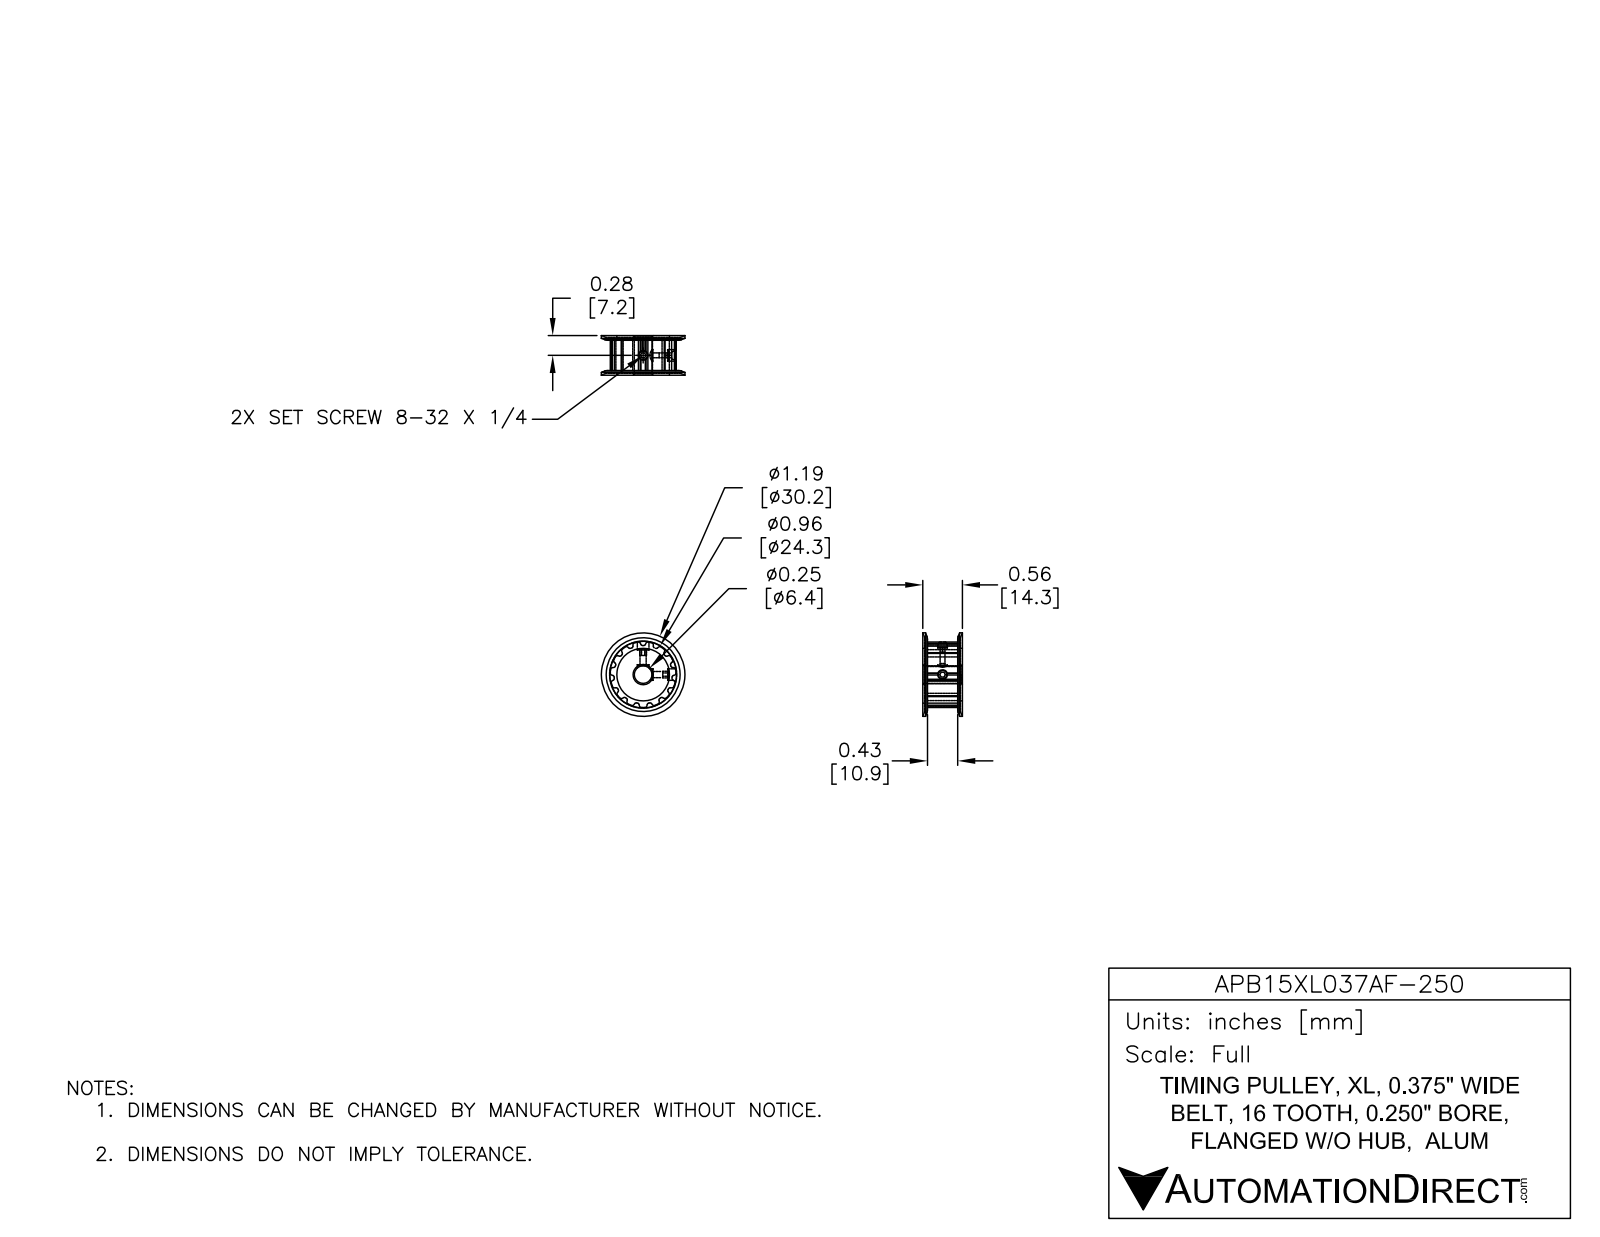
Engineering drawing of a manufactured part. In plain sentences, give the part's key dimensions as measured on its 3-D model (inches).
The part is named "APB15XL037AF-250". Its 3-D file was written by "SolidWorks 2014 (AUTOMOTIVE_DESIGN)". It is 1 solid with 188 faces: 52 planar, 116 cylindrical and 20 other. Overall it measures 1.188 by 1.188 by 0.563 inches. Its volume is 0.323 cubic inches and its surface area 5.648 square inches. Round holes: 2 of diameter 0.088, 1 of diameter 0.125, 1 of diameter 0.25. Round bosses or shafts: 1 of diameter 0.496. Partial cylindrical surfaces (rounded edges, fillets, slot ends): 59 of radius 0.015, 1 of radius 0.062, 1 of radius 0.413, 1 of radius 0.467, 1 of radius 0.468. The main face-to-face distances are 0.5, 0.031, 0.531, 0.063, 0.469, 0.563, 0.437.
